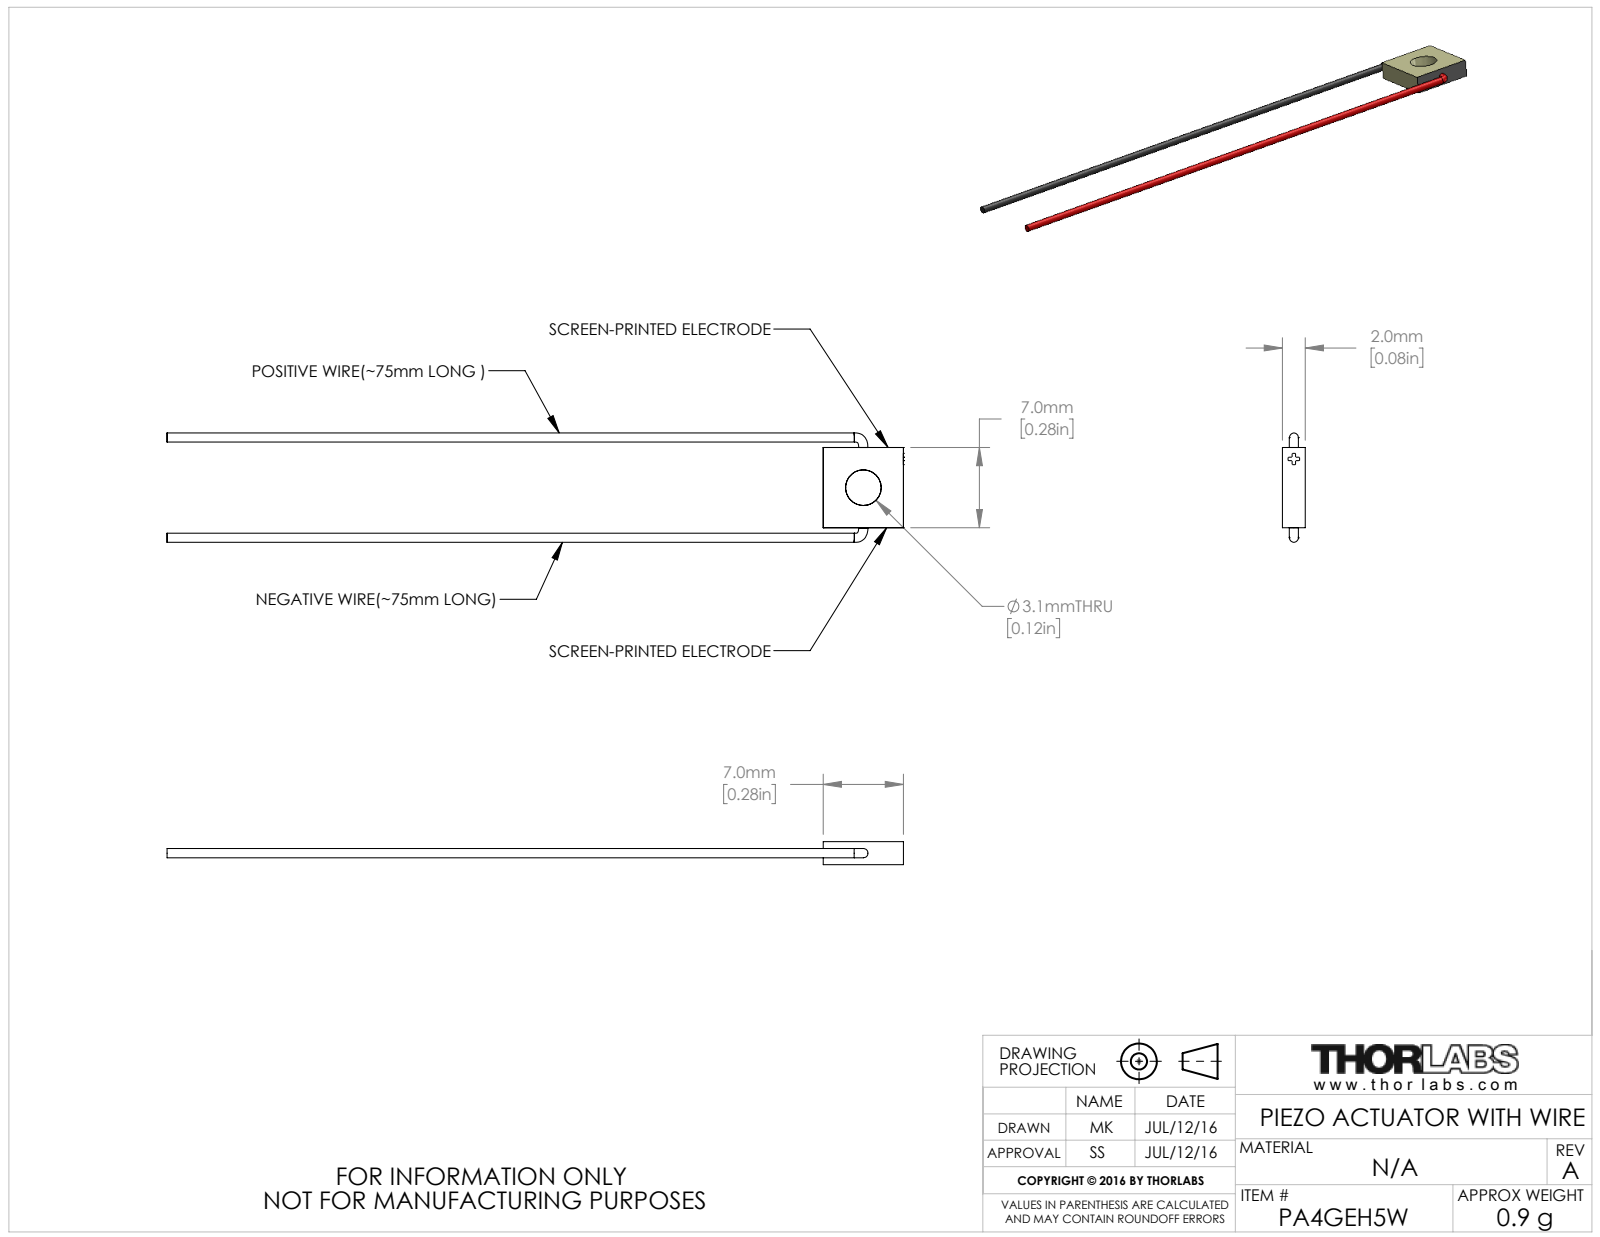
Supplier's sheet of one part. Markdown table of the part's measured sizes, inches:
| quantity | value |
| --- | --- |
| part name | CTN009264 |
| STEP written by | SolidWorks 2016 (AUTOMOTIVE_DESIGN) |
| units | inches |
| bodies | 3 solids, 21 faces (11 planar, 2 cylindrical, 8 other) |
| overall size | 2.531 × 0.376 × 0.079 |
| volume | 0.009 in³ |
| surface area | 0.727 in² |
| round holes (diameter × count) | 0.122 × 1 |
| main face-to-face distances | 0.079, 0.276, 2.531, 2.256 |
